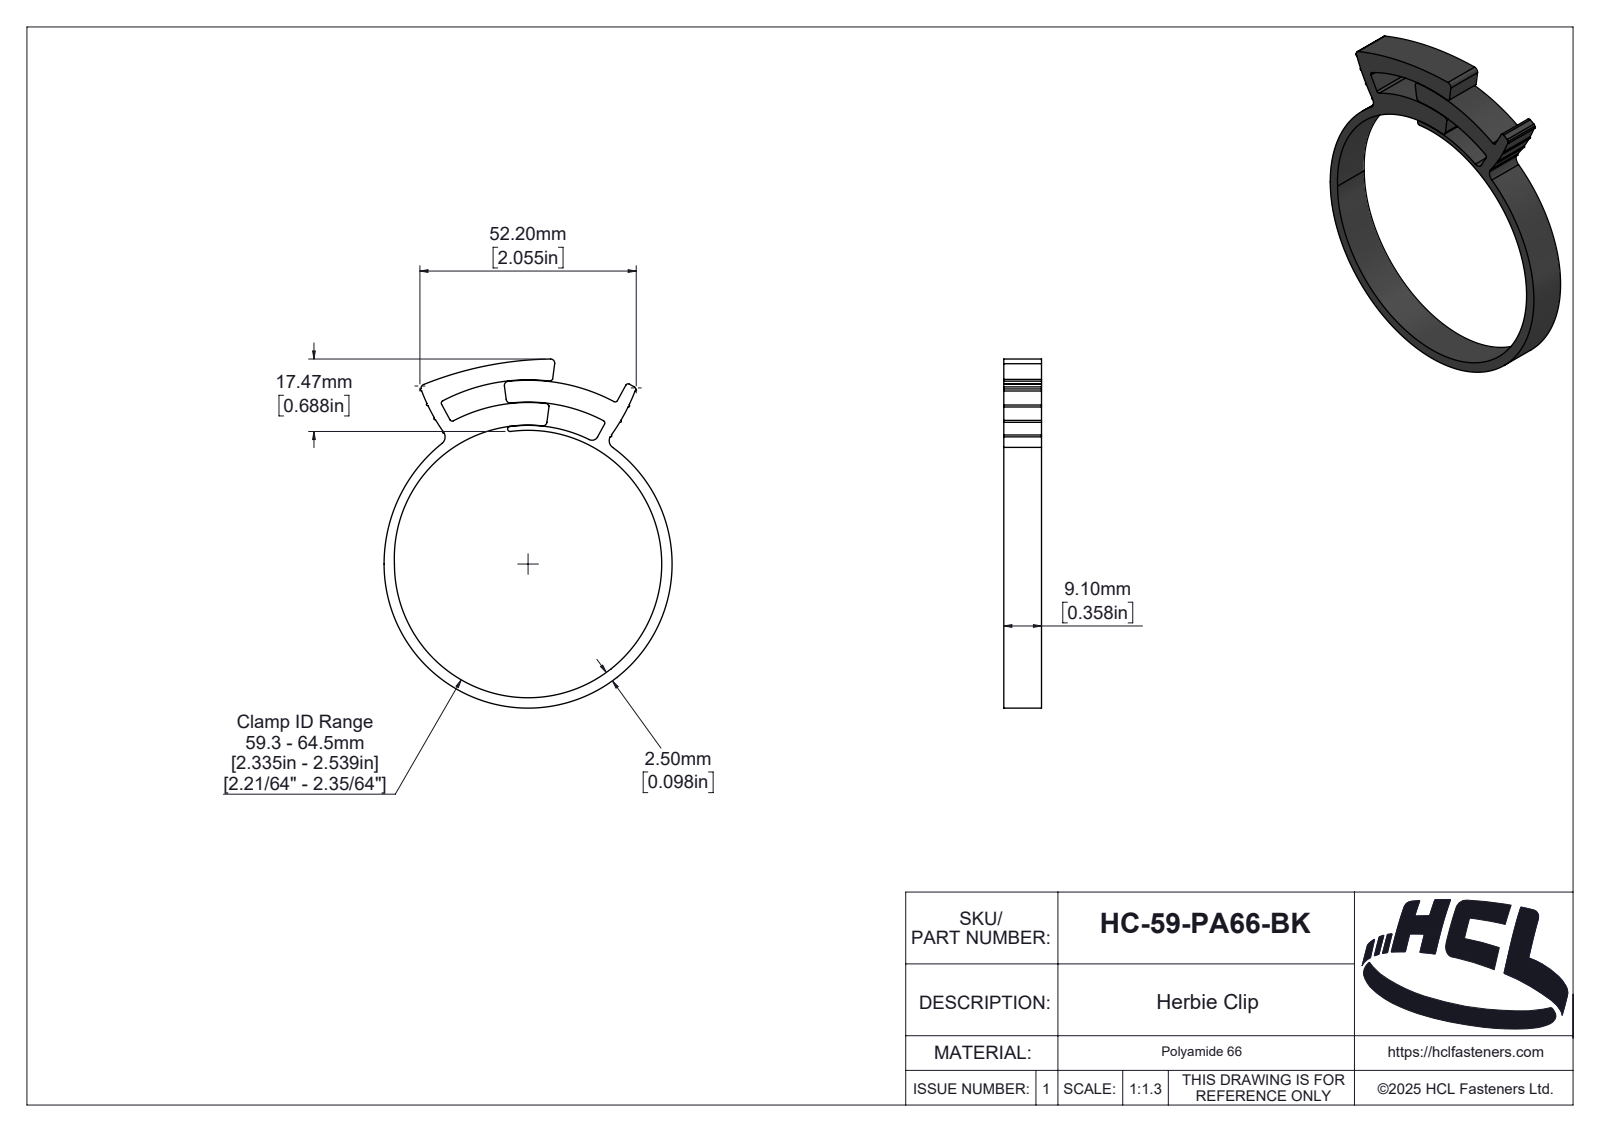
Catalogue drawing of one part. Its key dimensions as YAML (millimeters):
part_name: "HC-59-PA66-BK"
step_written_by: "SolidWorks 2025 (AUTOMOTIVE_DESIGN)"
units: millimeters
bodies: {solids: 1, faces: 162, planar: 13, cylindrical: 100, other: 49}
overall_size: [84.19, 69.5, 9.1]
volume: 8655
surface_area: 7495
partial_cylinders:
  - {radius: 0.25, count: 8}
  - {radius: 0.6, count: 7}
  - {radius: 1, count: 5}
  - {radius: 2, count: 2}
  - {radius: 0.17, count: 1}
  - {radius: 0.67, count: 1}
  - {radius: 0.84, count: 1}
  - {radius: 0.89, count: 1}
face_to_face_distances: [9.1]
